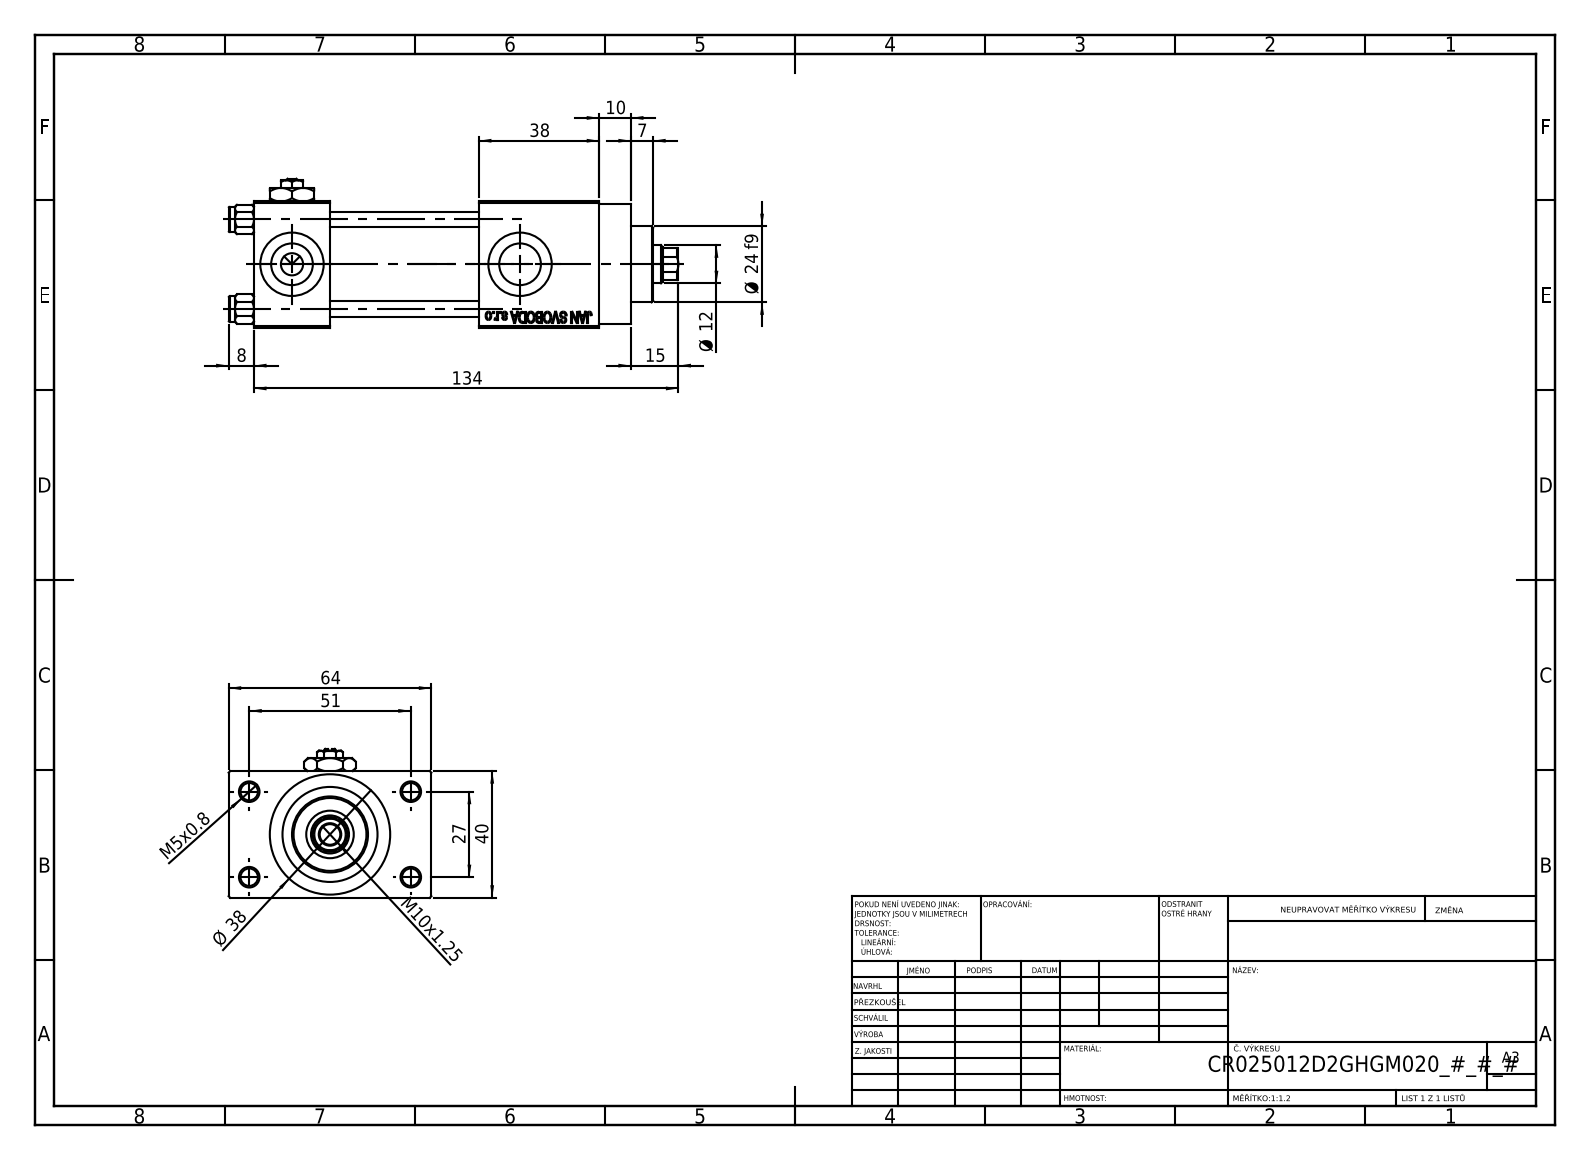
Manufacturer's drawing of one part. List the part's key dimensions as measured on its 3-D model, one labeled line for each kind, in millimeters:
Part name (STEP PRODUCT): V215CR_D_TYCINKA; V215CR_D_Body; V215CR_VCP_D; Zatka_pro_OIL_PORT (+2 more)
STEP written by: SolidWorks 2019 (CONFIG_CONTROL_DESIGN)
Units: millimetres
Bodies: 12 solids, 1154 faces (519 planar, 95 cylindrical, 540 other)
Overall size (bounding box): 142 × 64 × 47
Volume: 172 605 mm³ · Surface area: 63 244 mm²
Round holes (diameter × count): ⌀5 ×4, ⌀5.5 ×4, ⌀20 ×4, ⌀7 ×3, ⌀13.16 ×3, ⌀6.5 ×1, ⌀12 ×1, ⌀15 ×1, ⌀25 ×1, ⌀30 ×1
Round bosses / shafts (diameter × count): ⌀8 ×4, ⌀38 ×1, ⌀31 ×1, ⌀24 ×1
Partial cylindrical surfaces — rounded edges, fillets, slot ends (radius × count): R5.5 ×1
Main face-to-face distances: 40, 12, 47, 52, 24, 71, 38, 109, 85, 64
Hole centre spacings: 11.37, 20.01, 28.3, 28.85, 29.89, 39.66, 48.34, 27
